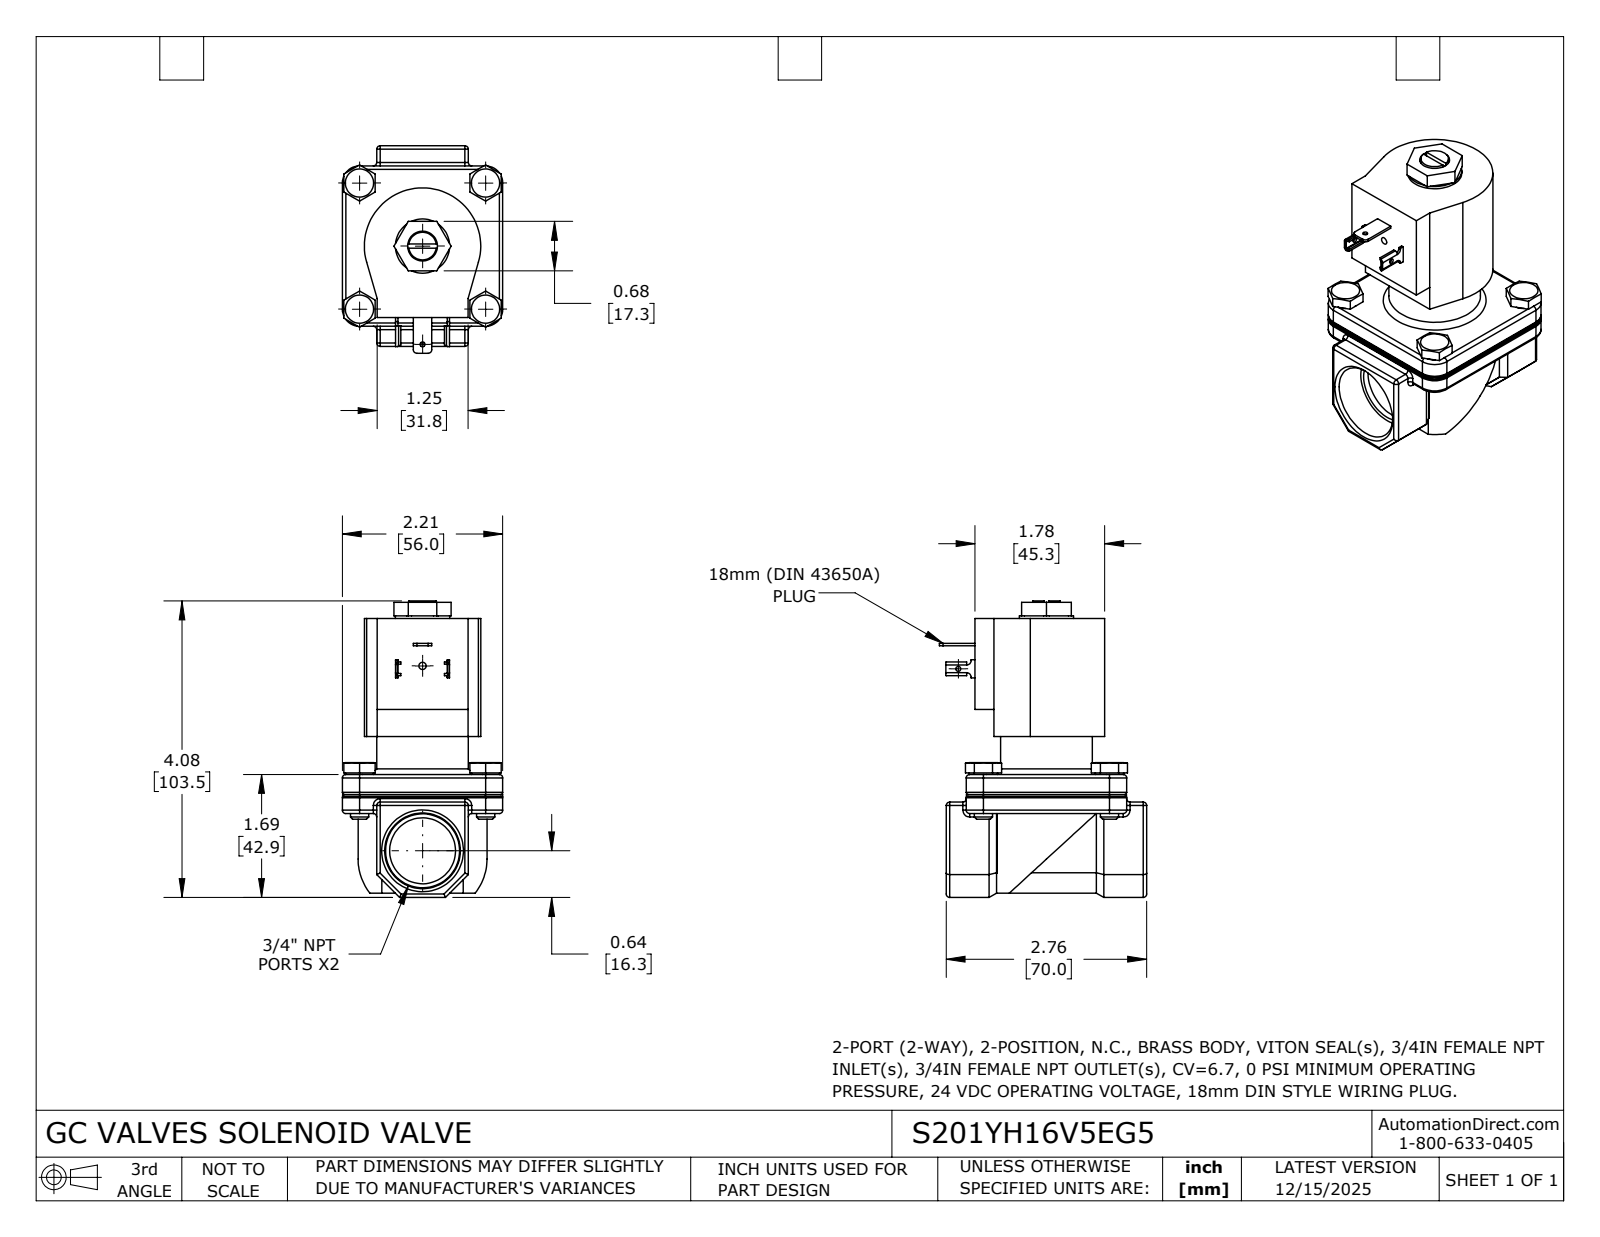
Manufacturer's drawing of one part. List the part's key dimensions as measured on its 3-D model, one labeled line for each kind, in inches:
Part name (STEP PRODUCT): S201YH16V5EG5
STEP written by: SolidWorks 2024 (CONFIG_CONTROL_DESIGN)
Units: inches
Bodies: 1 solid, 338 faces (166 planar, 112 cylindrical, 60 other)
Overall size (bounding box): 4.075 × 2.851 × 2.205
Volume: 10.16 in³ · Surface area: 43.84 in²
Round holes (diameter × count): ⌀0.066 ×1, ⌀0.067 ×1, ⌀0.1 ×1, ⌀0.41 ×1, ⌀0.906 ×1
Round bosses / shafts (diameter × count): ⌀0.388 ×4, ⌀0.25 ×4, ⌀1.26 ×1, ⌀0.746 ×1, ⌀0.38 ×1
Partial cylindrical surfaces — rounded edges, fillets, slot ends (radius × count): R0.047 ×34, R0.006 ×4, R0.031 ×4, R0.041 ×4, R0.234 ×4, R0.236 ×4, R0.05 ×2, R0.06 ×2
Main face-to-face distances: 0.059, 2.143, 0.472, 1.732, 0.537, 2.68, 2.205, 1.094, 1.631, 3.774
Hole centre spacings: 1.35, 2.541
